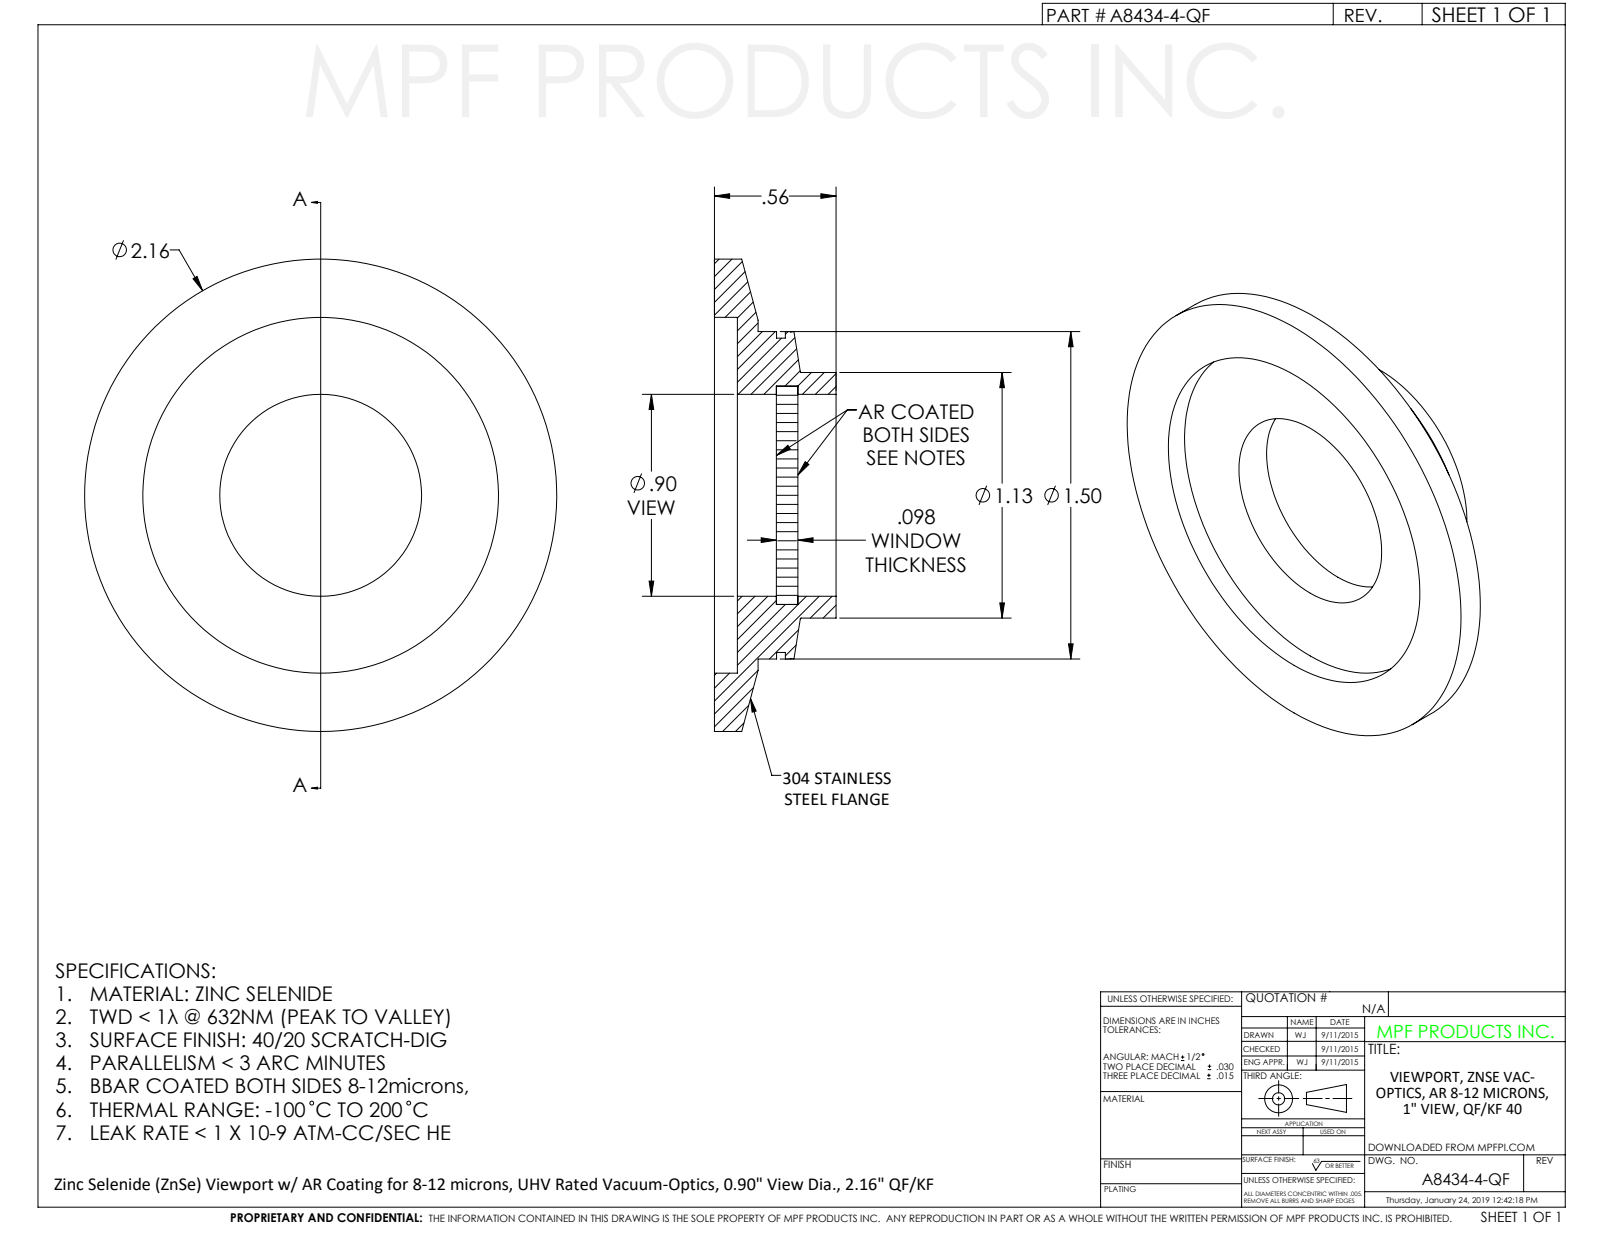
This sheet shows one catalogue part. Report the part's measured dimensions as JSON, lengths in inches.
{"part_name": "A8434-4-QF", "step_written_by": "SolidWorks 2012 (CONFIG_CONTROL_DESIGN)", "units": "inches", "bodies": {"solids": 1, "faces": 37, "planar": 9, "cylindrical": 16, "other": 12}, "overall_size": [2.165, 2.165, 0.557], "volume_in3": 0.706, "surface_area_in2": 11.43, "round_holes": [[0.925, 1], [1.63, 1]], "round_bosses_or_shafts": [[2.165, 1], [1.5, 1], [1.44, 1], [1.125, 1]], "face_to_face_distances": [0.105, 0.284, 0.382, 0.179, 0.277, 0.098, 0.557, 0.452, 0.274, 0.175]}
